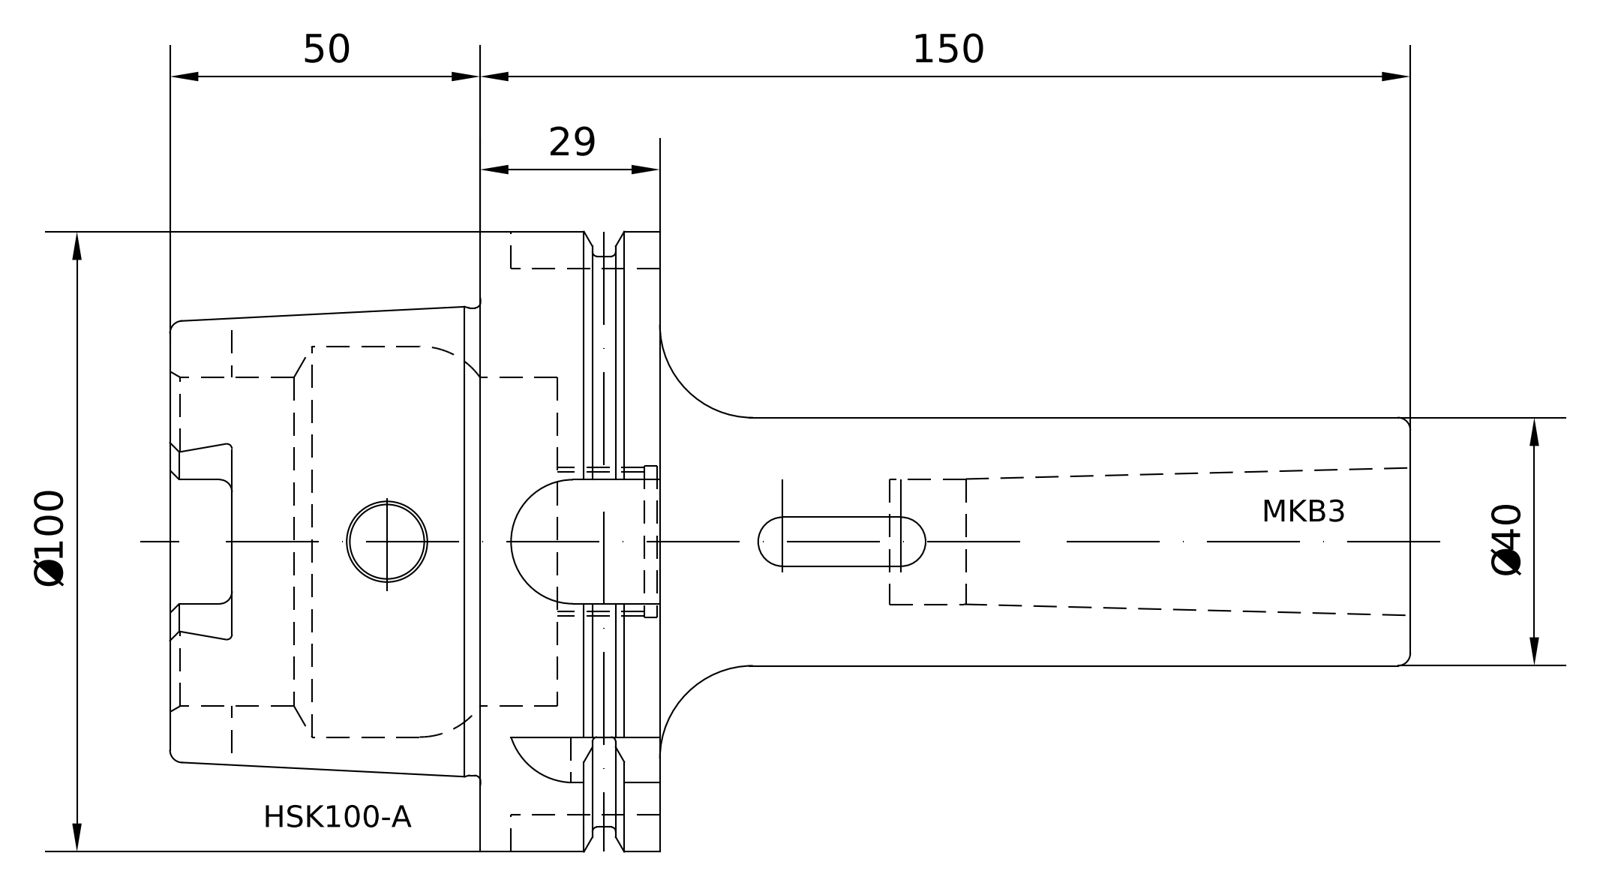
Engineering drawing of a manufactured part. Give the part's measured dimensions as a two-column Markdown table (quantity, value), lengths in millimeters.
| quantity | value |
| --- | --- |
| part name | A100-080-03 |
| STEP written by | PRO/ENGINEER BY PARAMETRIC TECHNOLOGY CORPORATION, 2010430 (CONFIG_CONTROL_DESIGN) |
| units | millimeters |
| bodies | 1 solid, 174 faces (50 planar, 51 cylindrical, 73 other) |
| overall size | 200 × 100 × 100 |
| volume | 381 921 mm³ |
| surface area | 70 241 mm² |
| round holes (diameter × count) | 10 × 1, 12 × 1, 20.2 × 1, 22.5 × 1, 24 × 1, 24.32 × 1, 24.5 × 1, 53 × 1, 63 × 1 |
| round bosses / shafts (diameter × count) | 100 × 1, 92 × 1, 75.36 × 1, 40 × 1 |
| partial cylindrical surfaces (radius × count) | 2 × 6, 5 × 4, 8 × 1, 10 × 1, 11 × 1 |
| main face-to-face distances | 29, 12.5, 16.5, 50, 62.5, 79, 200, 150, 137.5, 121 |
